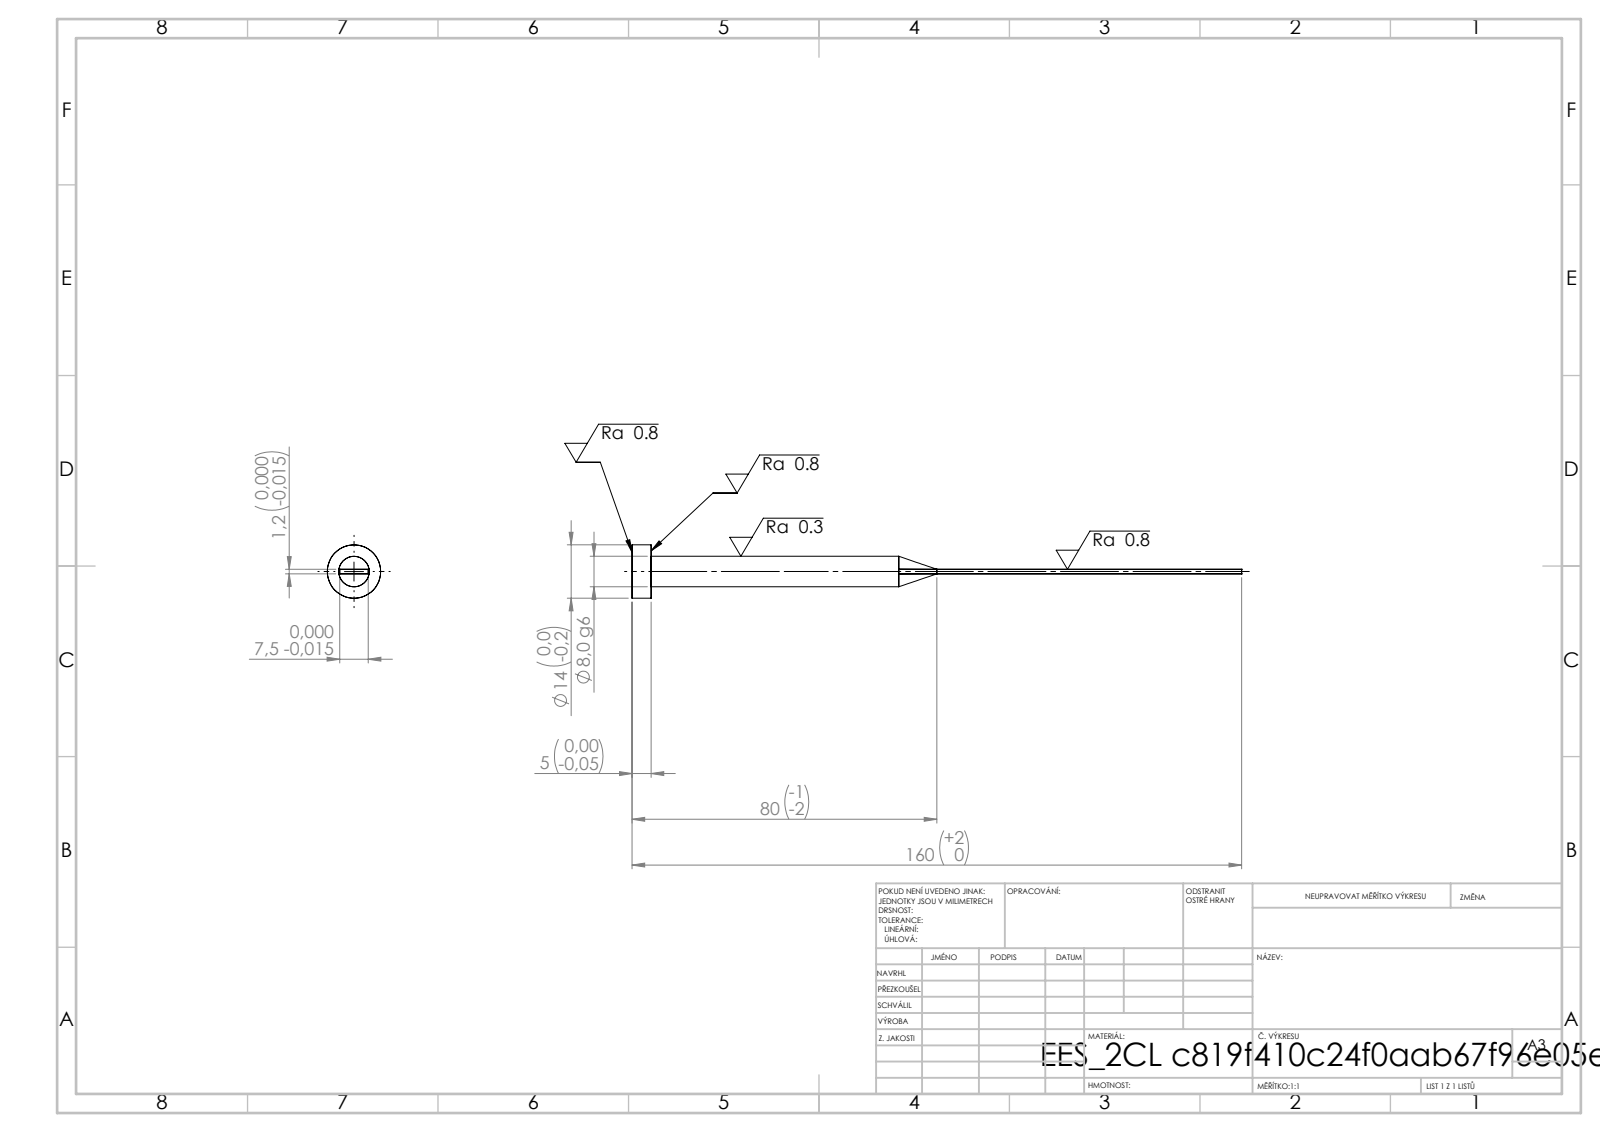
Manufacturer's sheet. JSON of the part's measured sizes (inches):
{"step_written_by": "SolidWorks 2019 (CONFIG_CONTROL_DESIGN)", "units": "inches", "bodies": {"solids": 1, "faces": 15, "planar": 7, "cylindrical": 4, "other": 4}, "overall_size": [6.299, 0.551, 0.551], "volume_in3": 0.307, "surface_area_in2": 5.766, "round_bosses_or_shafts": [[0.551, 1], [0.315, 1]], "face_to_face_distances": [0.047, 0.197, 0.295, 6.299, 6.102]}
